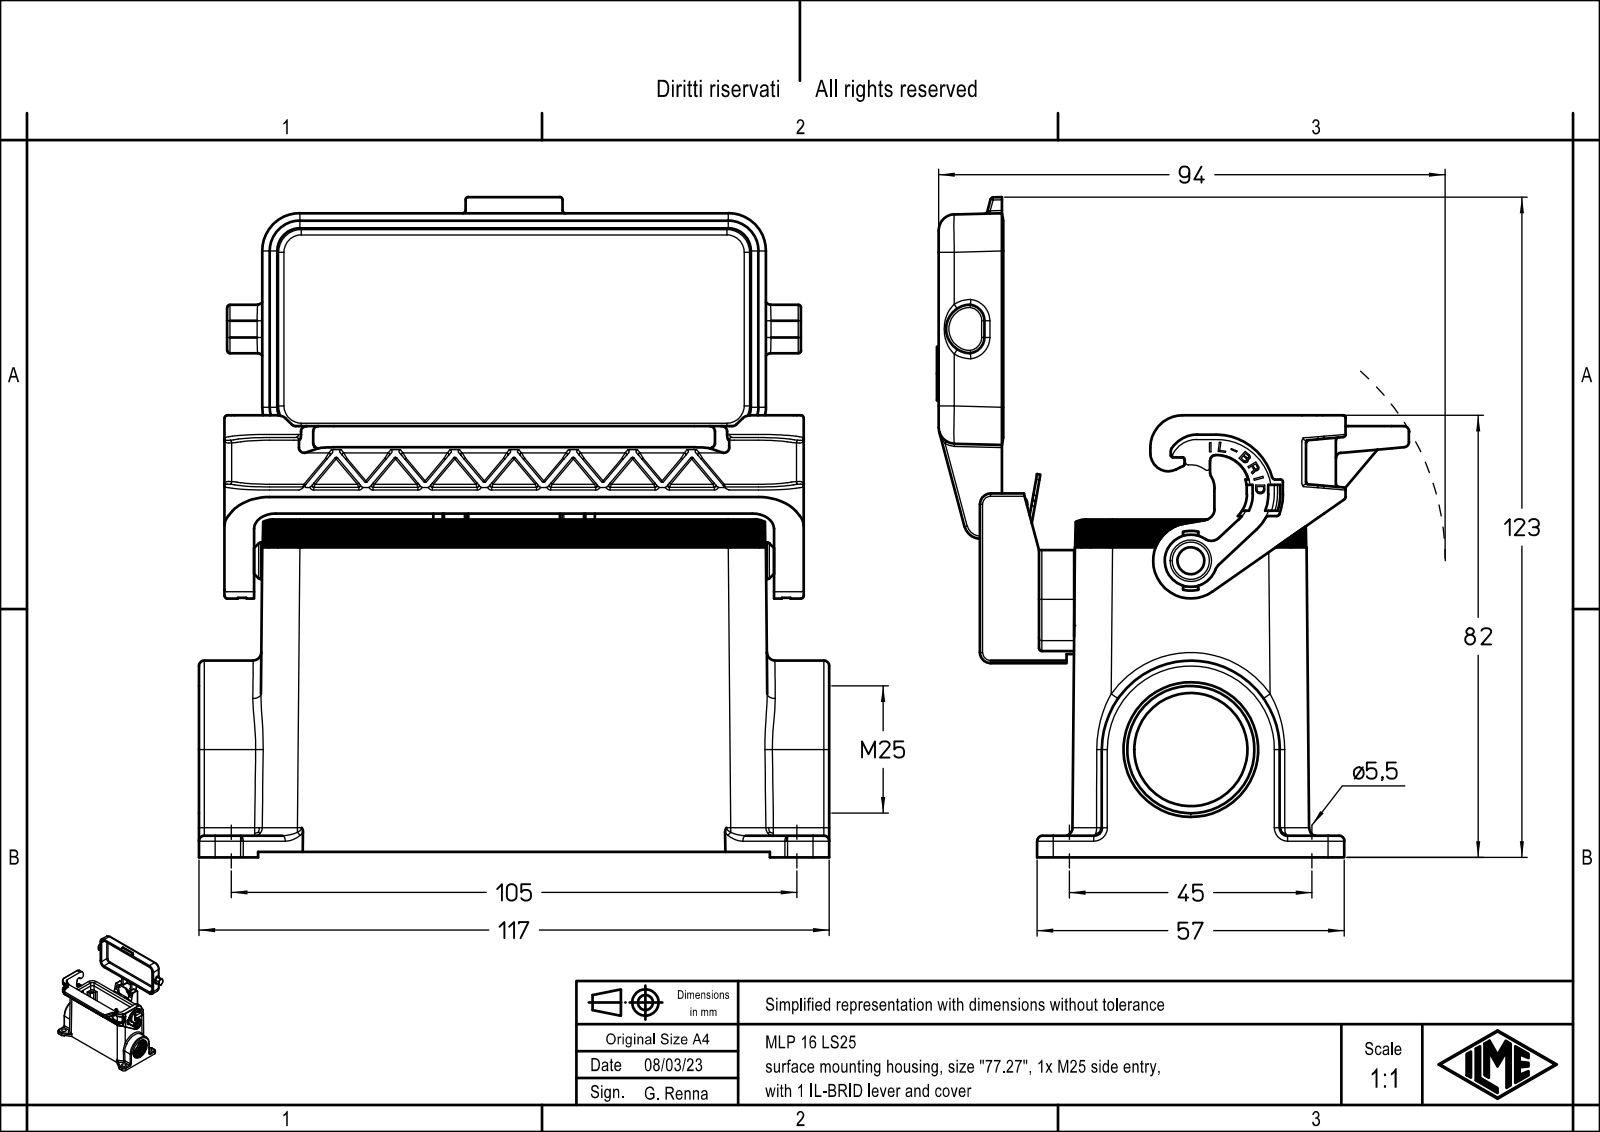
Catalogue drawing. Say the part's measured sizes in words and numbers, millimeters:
The part is named "MLP 16 LS25". Its 3-D file was written by "Creo Elements/Direct Modeling 20.1B 02-Apr-2019 (C) Parametric Technology GmbH (AUTOMOTIVE_DESIGN)". It is 1 solid with 1398 faces: 817 planar, 404 cylindrical and 177 other. Overall it measures 122.49 by 117 by 87.8 millimeters. Its volume is 139 294 cubic millimeters and its surface area 79 988 square millimeters. Round holes: 4 of diameter 3, 4 of diameter 3.5, 4 of diameter 5.5, 1 of diameter 3.25, 1 of diameter 4.2, 1 of diameter 5.4, 1 of diameter 7.7, 1 of diameter 21, 1 of diameter 23.6. Round bosses or shafts: 1 of diameter 8.4, 1 of diameter 6.9, 1 of diameter 6.8, 1 of diameter 5.2, 1 of diameter 4, 1 of diameter 3.2. Partial cylindrical surfaces (rounded edges, fillets, slot ends): 28 of radius 0.5, 27 of radius 0.1, 27 of radius 1, 23 of radius 0.2, 23 of radius 3, 17 of radius 0.17, 16 of radius 0.33, 15 of radius 1.5. The main face-to-face distances are 2, 3, 2.8, 69.75, 71.75, 10.25, 106.75, 1, 79, 76. The hole center spacings are 16.43, 38.54, 91.69, 98.09, 27, 45, 77.5, 82.07.
